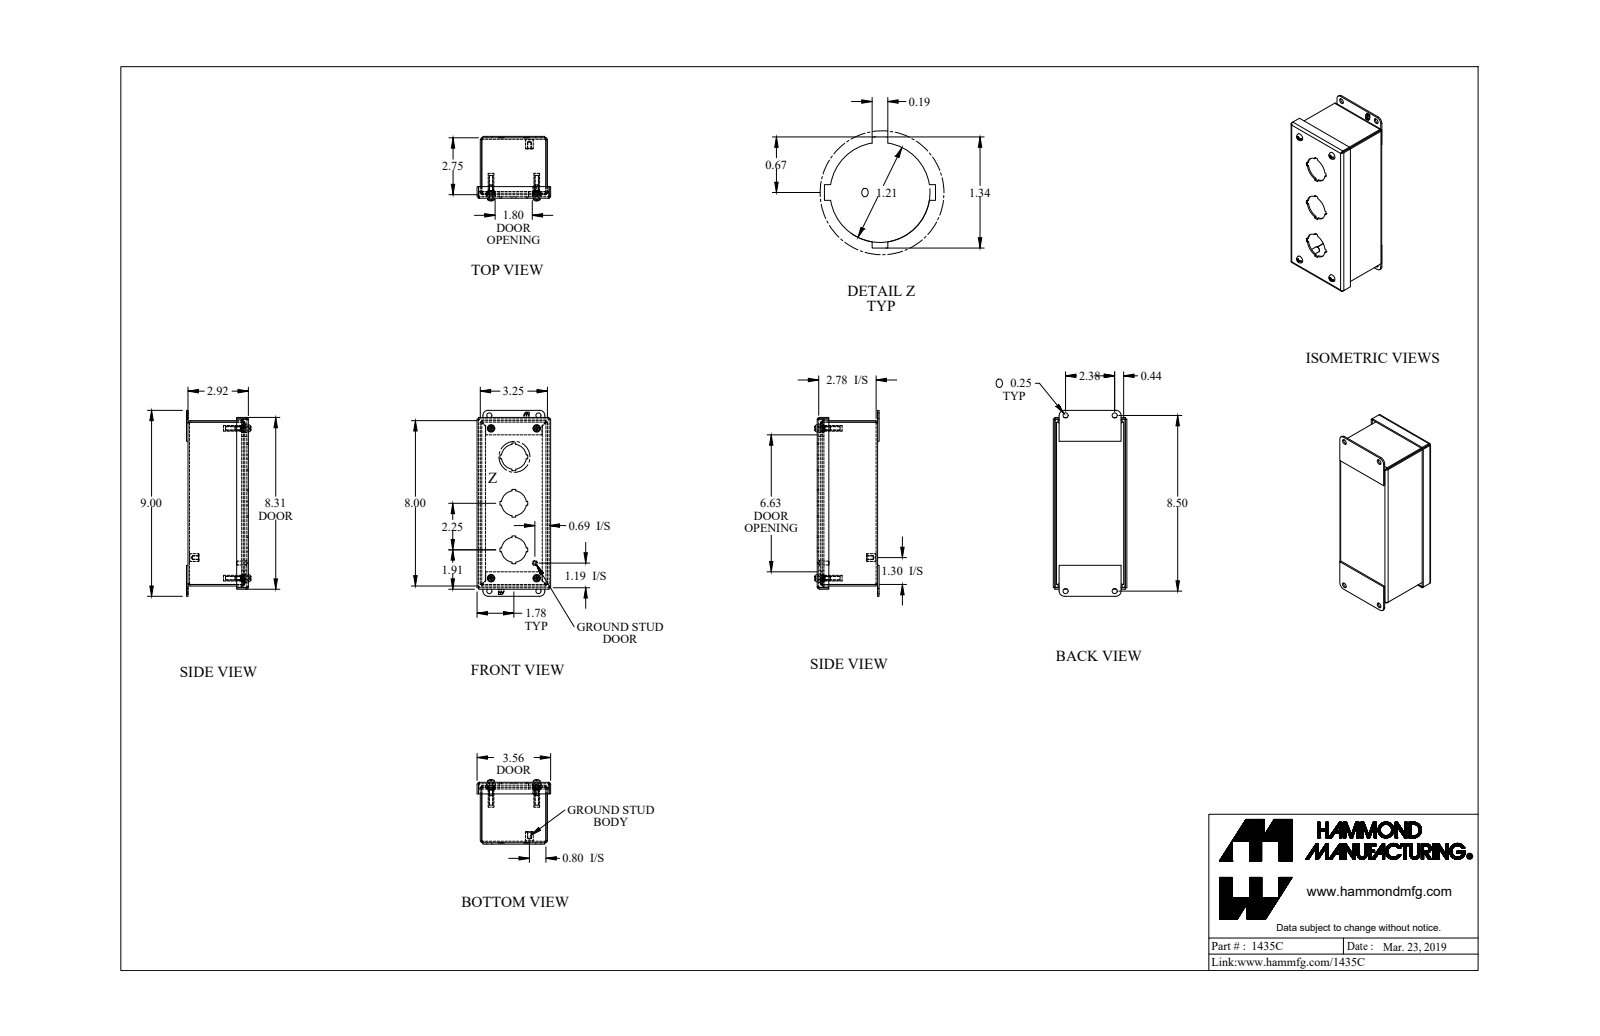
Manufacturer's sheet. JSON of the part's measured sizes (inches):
{"part_name": "1435C_Default", "step_written_by": "SolidWorks 2019 (CONFIG_CONTROL_DESIGN)", "units": "inches", "bodies": {"solids": 19, "faces": 603, "planar": 395, "cylindrical": 152, "other": 56}, "overall_size": [9, 3.562, 3.121], "volume_in3": 12.16, "surface_area_in2": 317.7, "round_holes": [[0.25, 8], [0.159, 4], [0.406, 4], [1.21, 3], [0.156, 1]], "round_bosses_or_shafts": [[0.39, 4], [0.275, 4], [0.19, 4], [0.148, 4], [0.375, 1], [0.25, 1], [0.188, 1]], "partial_cylinders_radius": [[0.036, 12], [0.108, 12], [0.16, 4], [0.171, 4], [0.25, 4], [0.125, 2]], "face_to_face_distances": [0.072, 2.85, 0.072, 3.178, 2.922, 2.778, 3.106, 3.25, 7.928, 0.156], "hole_center_spacings": [7.25, 7.58, 0.63, 1.765, 2.21, 2.211, 2.326, 3.79]}
